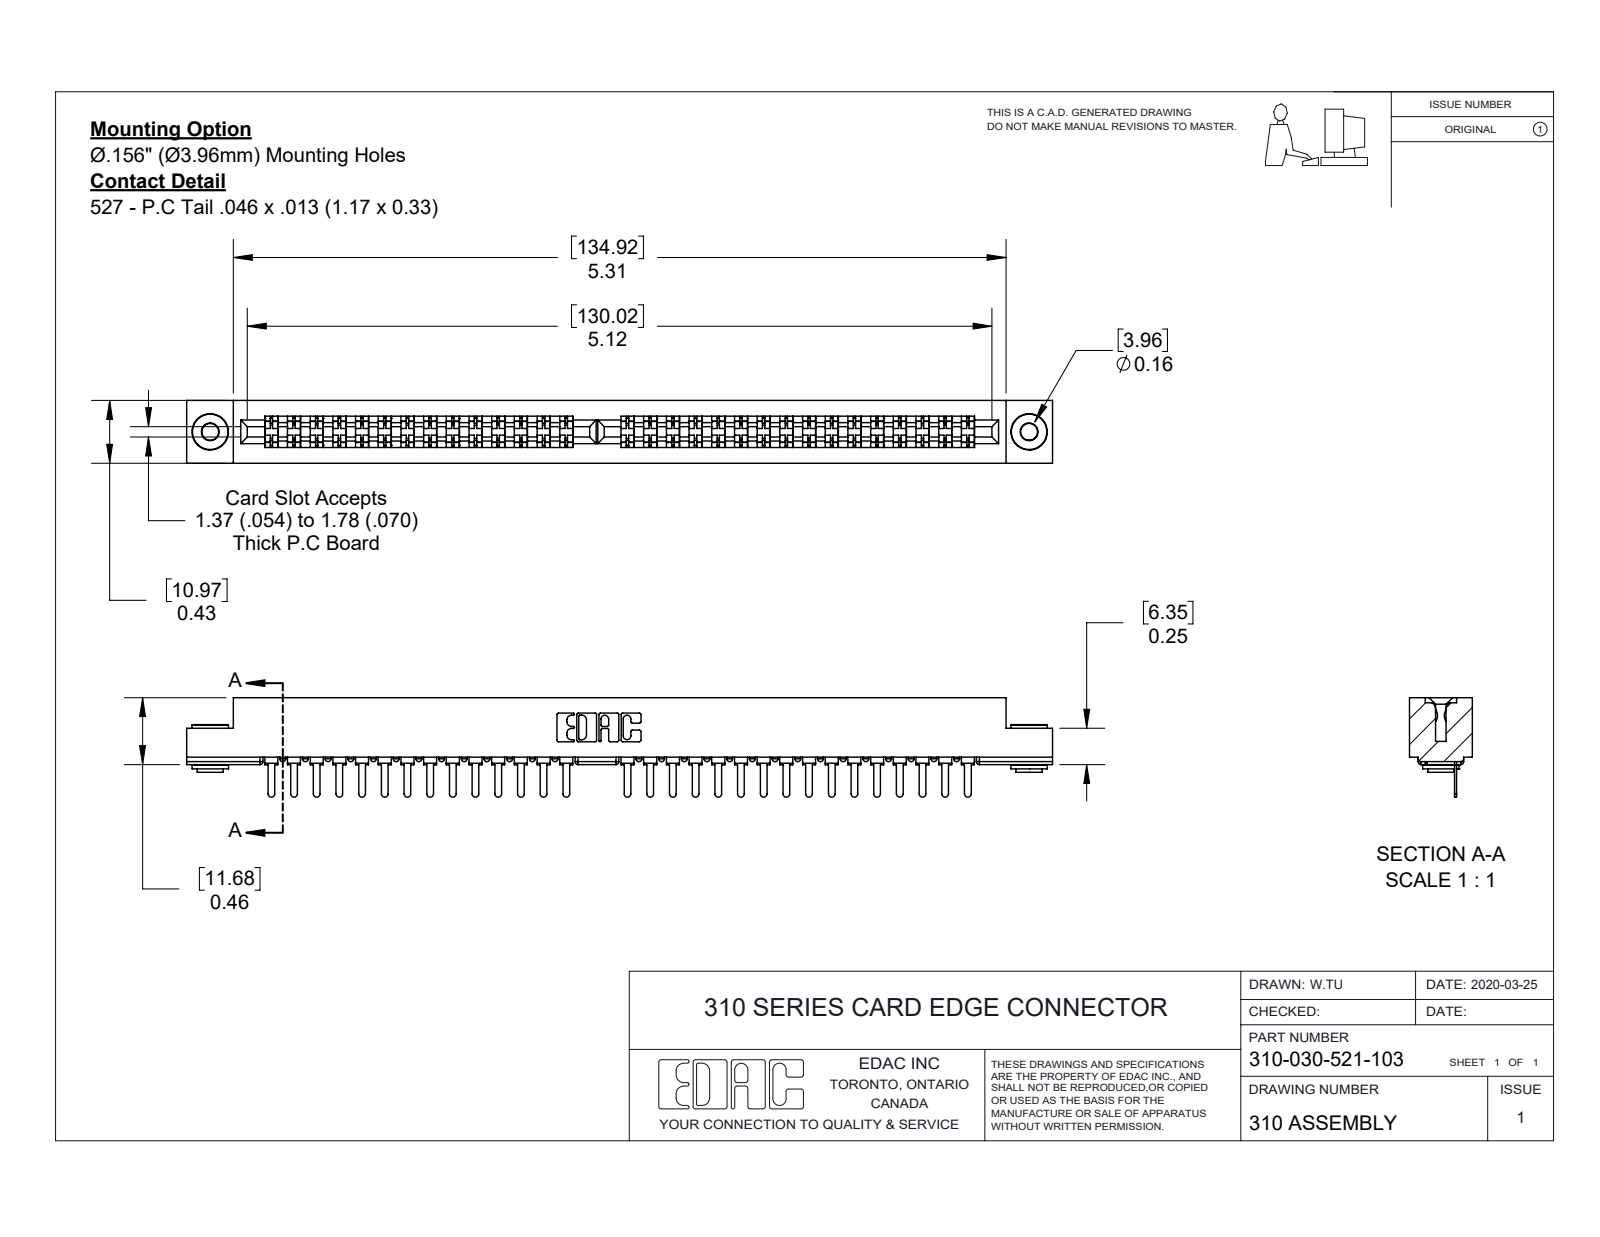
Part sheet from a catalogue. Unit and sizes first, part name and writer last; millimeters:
Units: millimetres
Overall size (bounding box): 151.21 × 17.37 × 10.97
Round holes (diameter × count): ⌀2.95 ×2, ⌀3.96 ×2
Round bosses / shafts (diameter × count): ⌀6.35 ×2, ⌀4.57 ×2, ⌀3.45 ×2
Partial cylindrical surfaces — rounded edges, fillets, slot ends (radius × count): R0.51 ×98, R0.58 ×30, R0.25 ×22, R0.17 ×6, R0.8 ×6, R0.67 ×3, R0.31 ×2, R0.64 ×2
Main face-to-face distances: 2.76, 8.22, 0.33, 10.98, 3.09, 7.89, 5.13, 5.46, 1.24, 3.89
Hole centre spacings: 143
Volume: 13 105 mm³ · Surface area: 18 639 mm²
Bodies: 33 solids, 2438 faces (1458 planar, 908 cylindrical, 72 other)
Part name (STEP PRODUCT): 310 Part_.116 Hex; 345-250-002_345-250-002-102; 307-290-002_521; 310-030-521-103
STEP written by: SolidWorks 2016 (CONFIG_CONTROL_DESIGN)
